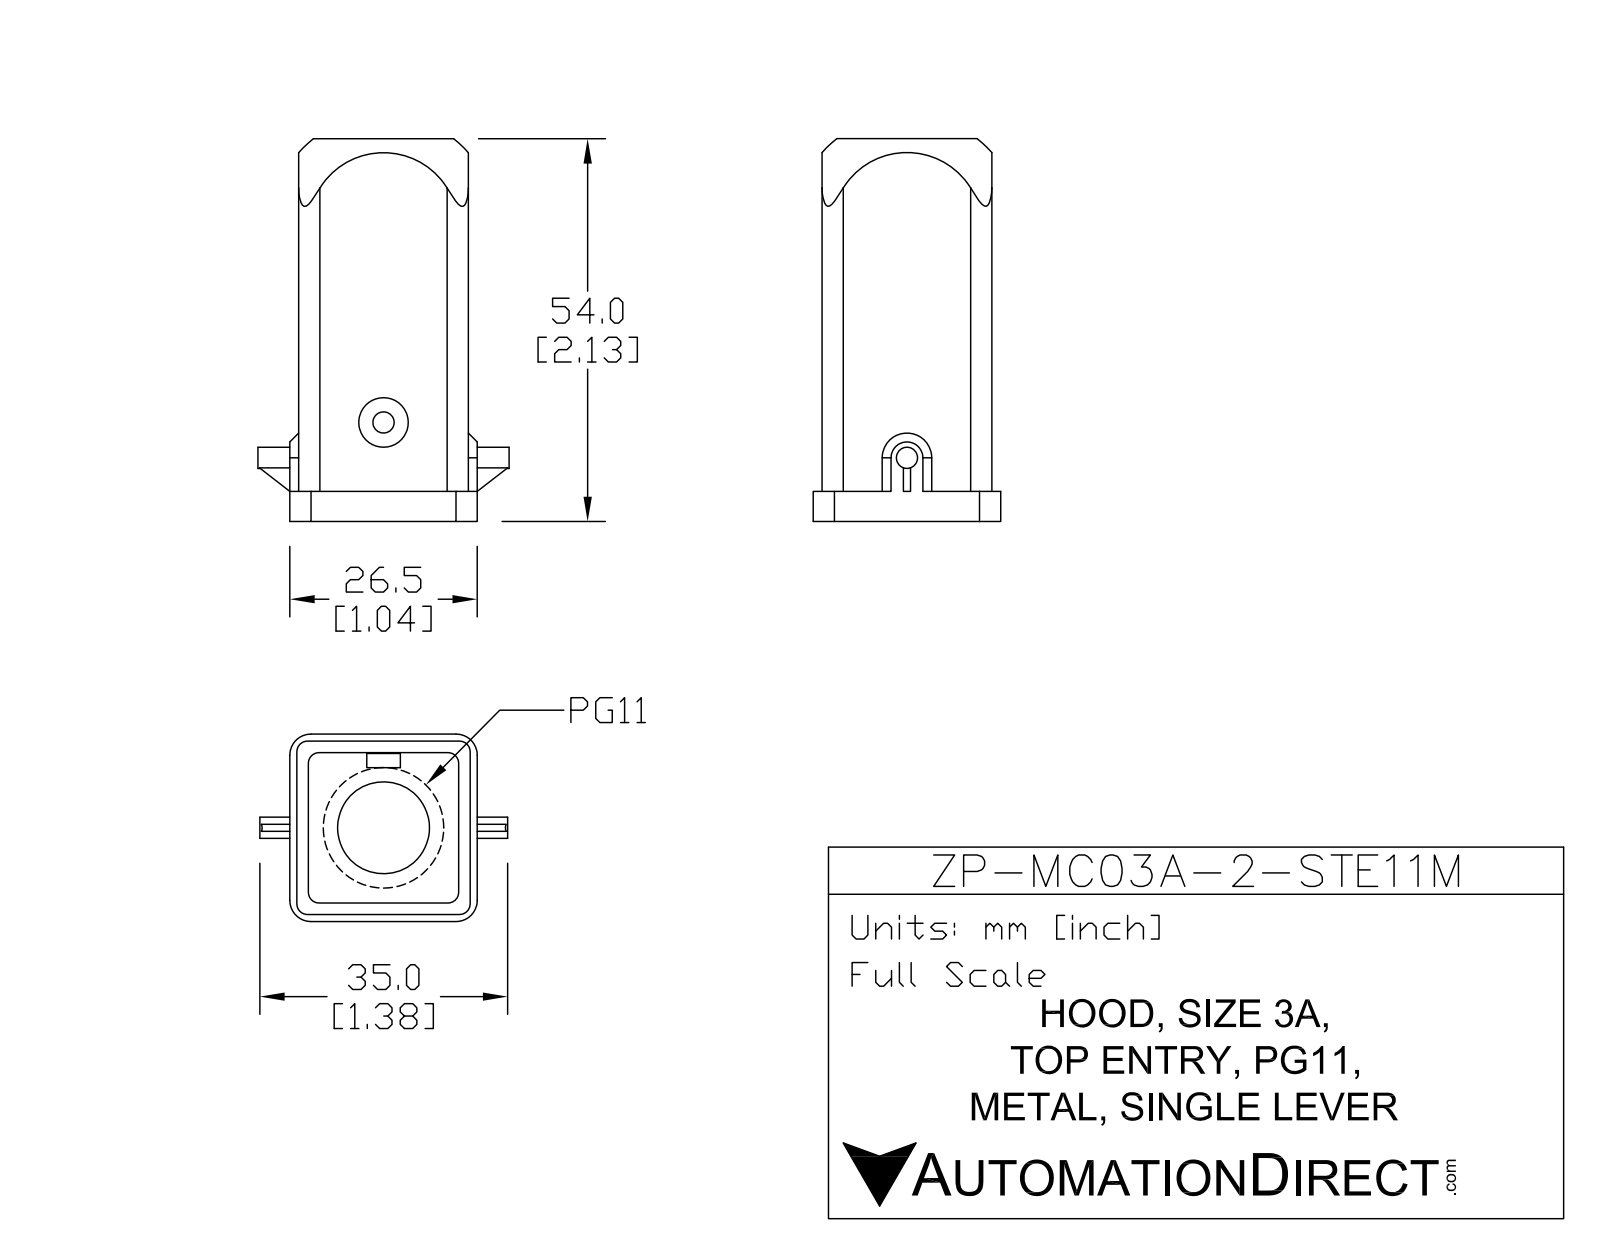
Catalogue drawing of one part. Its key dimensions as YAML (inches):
part_name: "ZP-MC03A-2-STE11M"
step_written_by: "SolidWorks 2011 (AUTOMOTIVE_DESIGN)"
units: inches
bodies: {solids: 1, faces: 65, planar: 40, cylindrical: 21, other: 4}
overall_size: [2.122, 1.398, 1.043]
volume: 0.568
surface_area: 15.75
round_holes:
  - {diameter: 0.118, count: 1}
  - {diameter: 0.512, count: 1}
  - {diameter: 0.669, count: 1}
round_bosses_or_shafts:
  - {diameter: 0.118, count: 1}
partial_cylinders:
  - {radius: 0.059, count: 8}
  - {radius: 0.118, count: 8}
face_to_face_distances: [0.054, 0.891, 0.945, 0.837, 0.049, 0.103, 0.94, 0.994, 0.039, 1.004]
